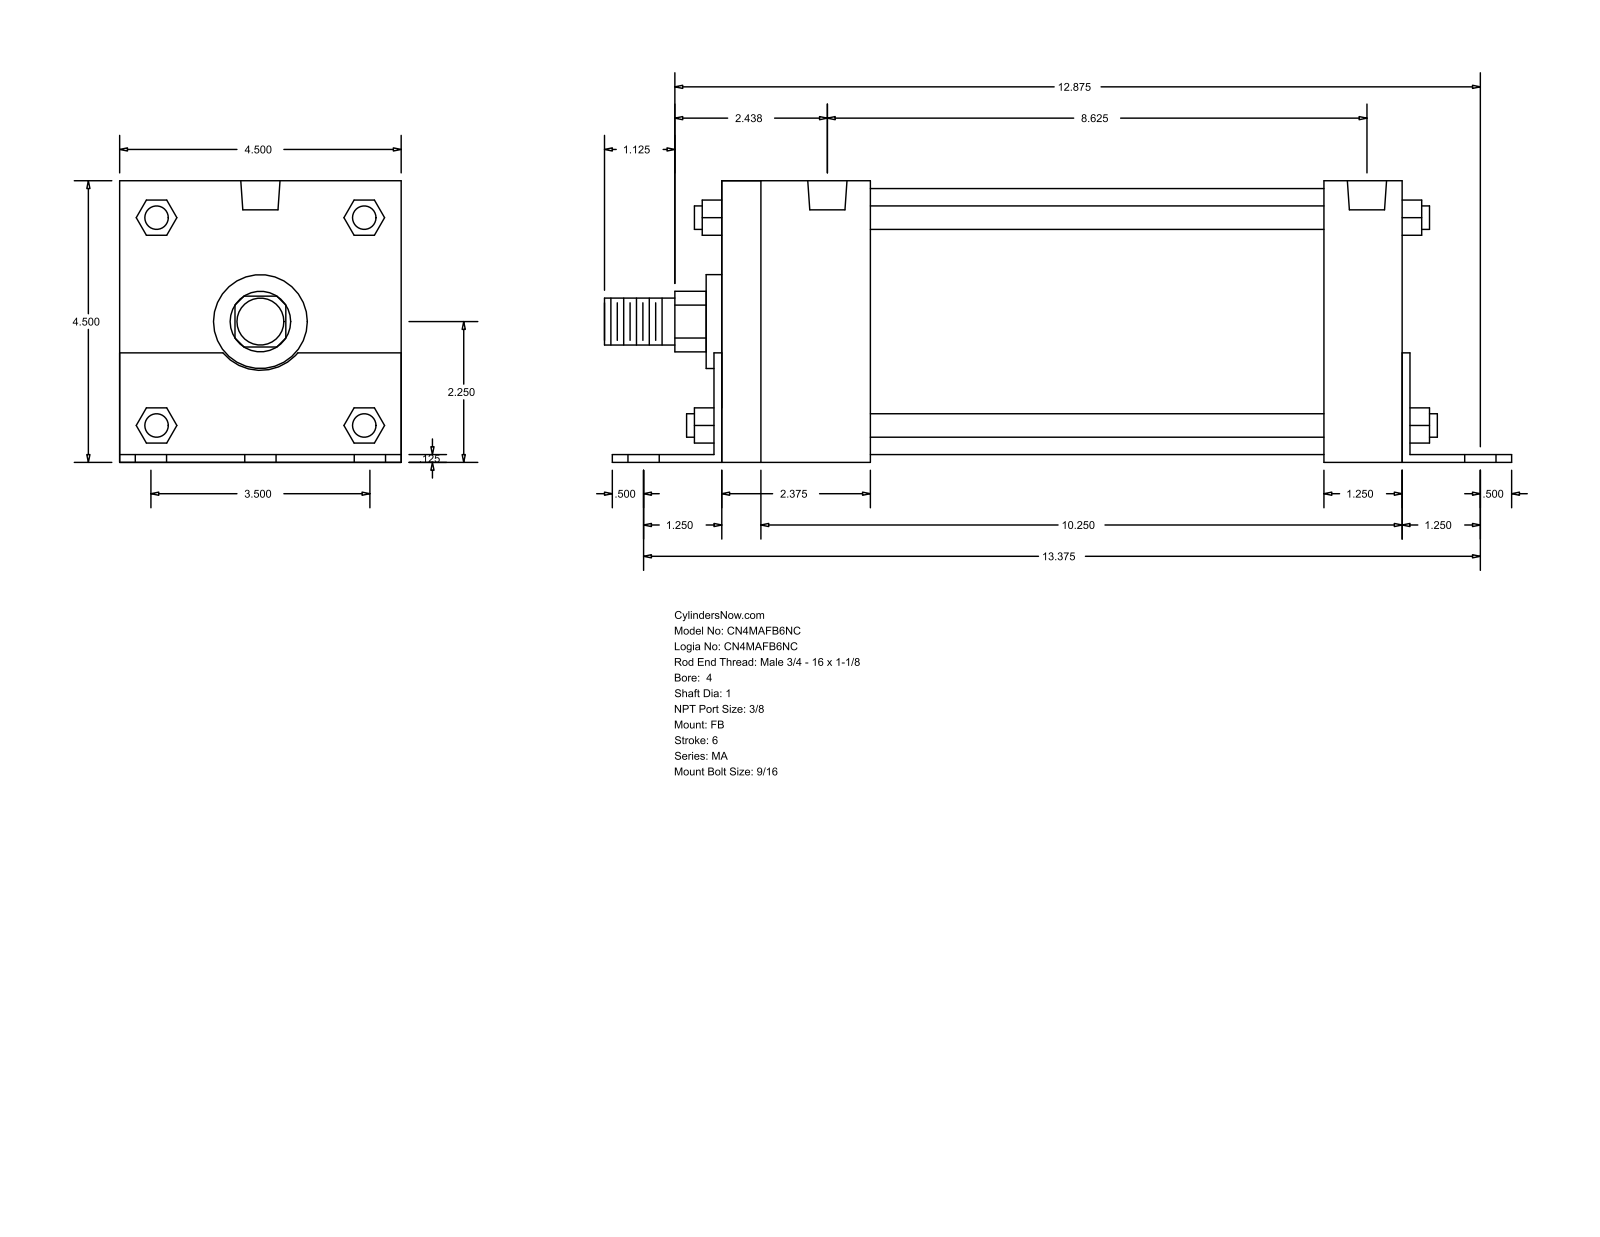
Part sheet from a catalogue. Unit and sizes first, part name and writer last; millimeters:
Units: millimetres
Overall size (bounding box): 368.3 × 114.35 × 114.3
Round holes (diameter × count): ⌀14.29 ×6, ⌀11.11 ×4, ⌀15.93 ×2
Round bosses / shafts (diameter × count): ⌀9.53 ×4, ⌀107.95 ×1, ⌀38.1 ×1, ⌀25.4 ×1, ⌀19.05 ×1
Partial cylindrical surfaces — rounded edges, fillets, slot ends (radius × count): R12.29 ×1, R19.81 ×1
Main face-to-face distances: 114.3, 3.17, 114.35, 3.12, 111.18, 276.22, 3.18, 282.57, 279.4, 279.39
Hole centre spacings: 44.45, 342.62, 339.72, 4.76, 63.99, 67.49, 86.85, 88.9
Bodies: 0 solids, 140 faces (105 planar, 35 cylindrical, 0 other)
Part name (STEP PRODUCT): MA_FB__0400_1
STEP written by: GSSL Pune (CONFIG_CONTROL_DESIGN)
